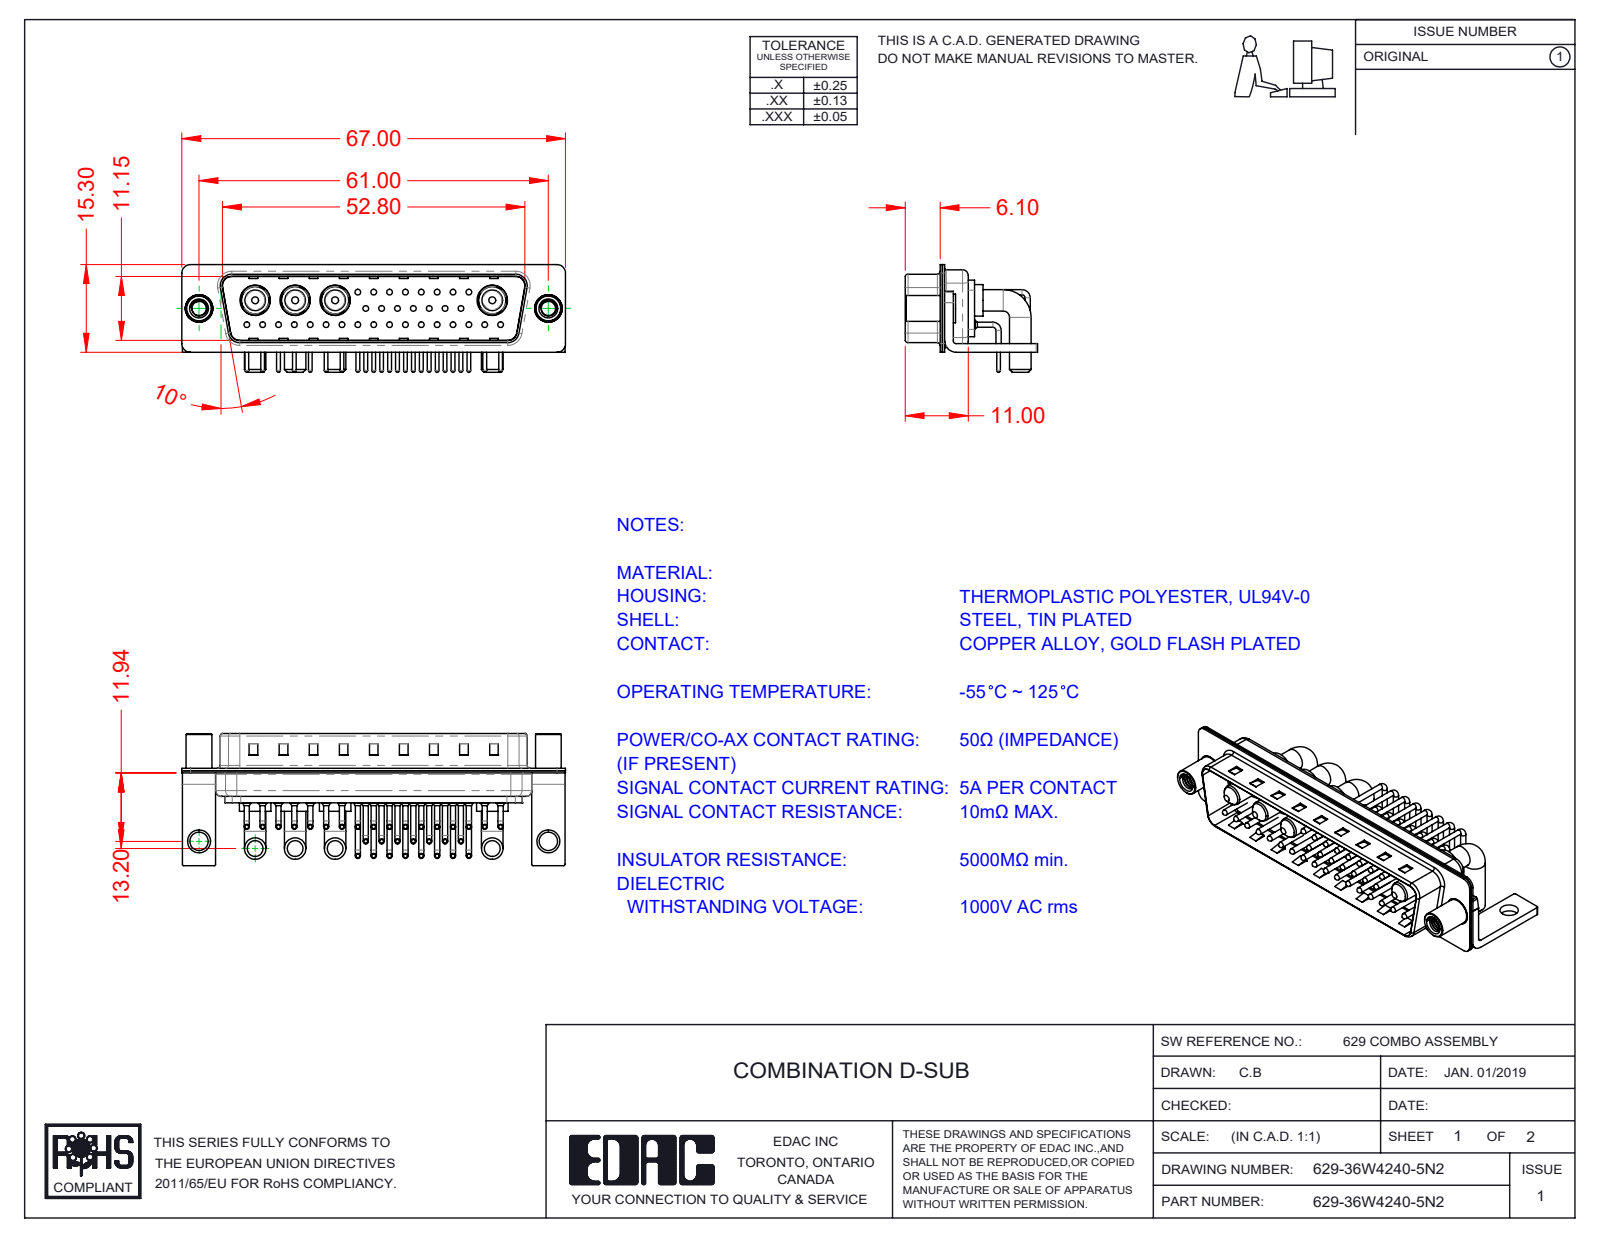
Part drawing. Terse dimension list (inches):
name: 629Combo Shell Front_50 Contacts; 629Combo Contact Row 3; Power Pin_40A RA 50; 629Combo Threaded Standoff_D (+6 more)
written by: SolidWorks 2020 (CONFIG_CONTROL_DESIGN)
unit: in
bodies: 47 solids, 4202 faces (2313 planar, 1449 cylindrical, 440 other)
size: 2.638 × 0.909 × 0.74
volume: 0.38 in³; area: 21.15 in²
holes: 32× ⌀0.03, 32× ⌀0.063, 32× ⌀0.079, 4× ⌀0.191, 4× ⌀0.209, 2× ⌀0.098, 2× ⌀0.126, 2× ⌀0.157, 2× ⌀0.189
bosses: 64× ⌀0.035, 32× ⌀0.059, 32× ⌀0.039, 32× ⌀0.026, 8× ⌀0.148, 4× ⌀0.217, 4× ⌀0.205, 4× ⌀0.187
rounds: 32× R0.04, 16× R0.01, 16× R0.059, 13× R0.079, 9× R0.02, 8× R0.063, 4× R0.024, 4× R0.026
face distances: 0.016, 0.059, 0.455, 0.22, 0.205, 0.031, 0.236, 0.031, 0.075, 0.043
hole spacings: 0.109, 0.218, 0.124, 0.327, 0.436, 0.545, 0.654, 0.763
